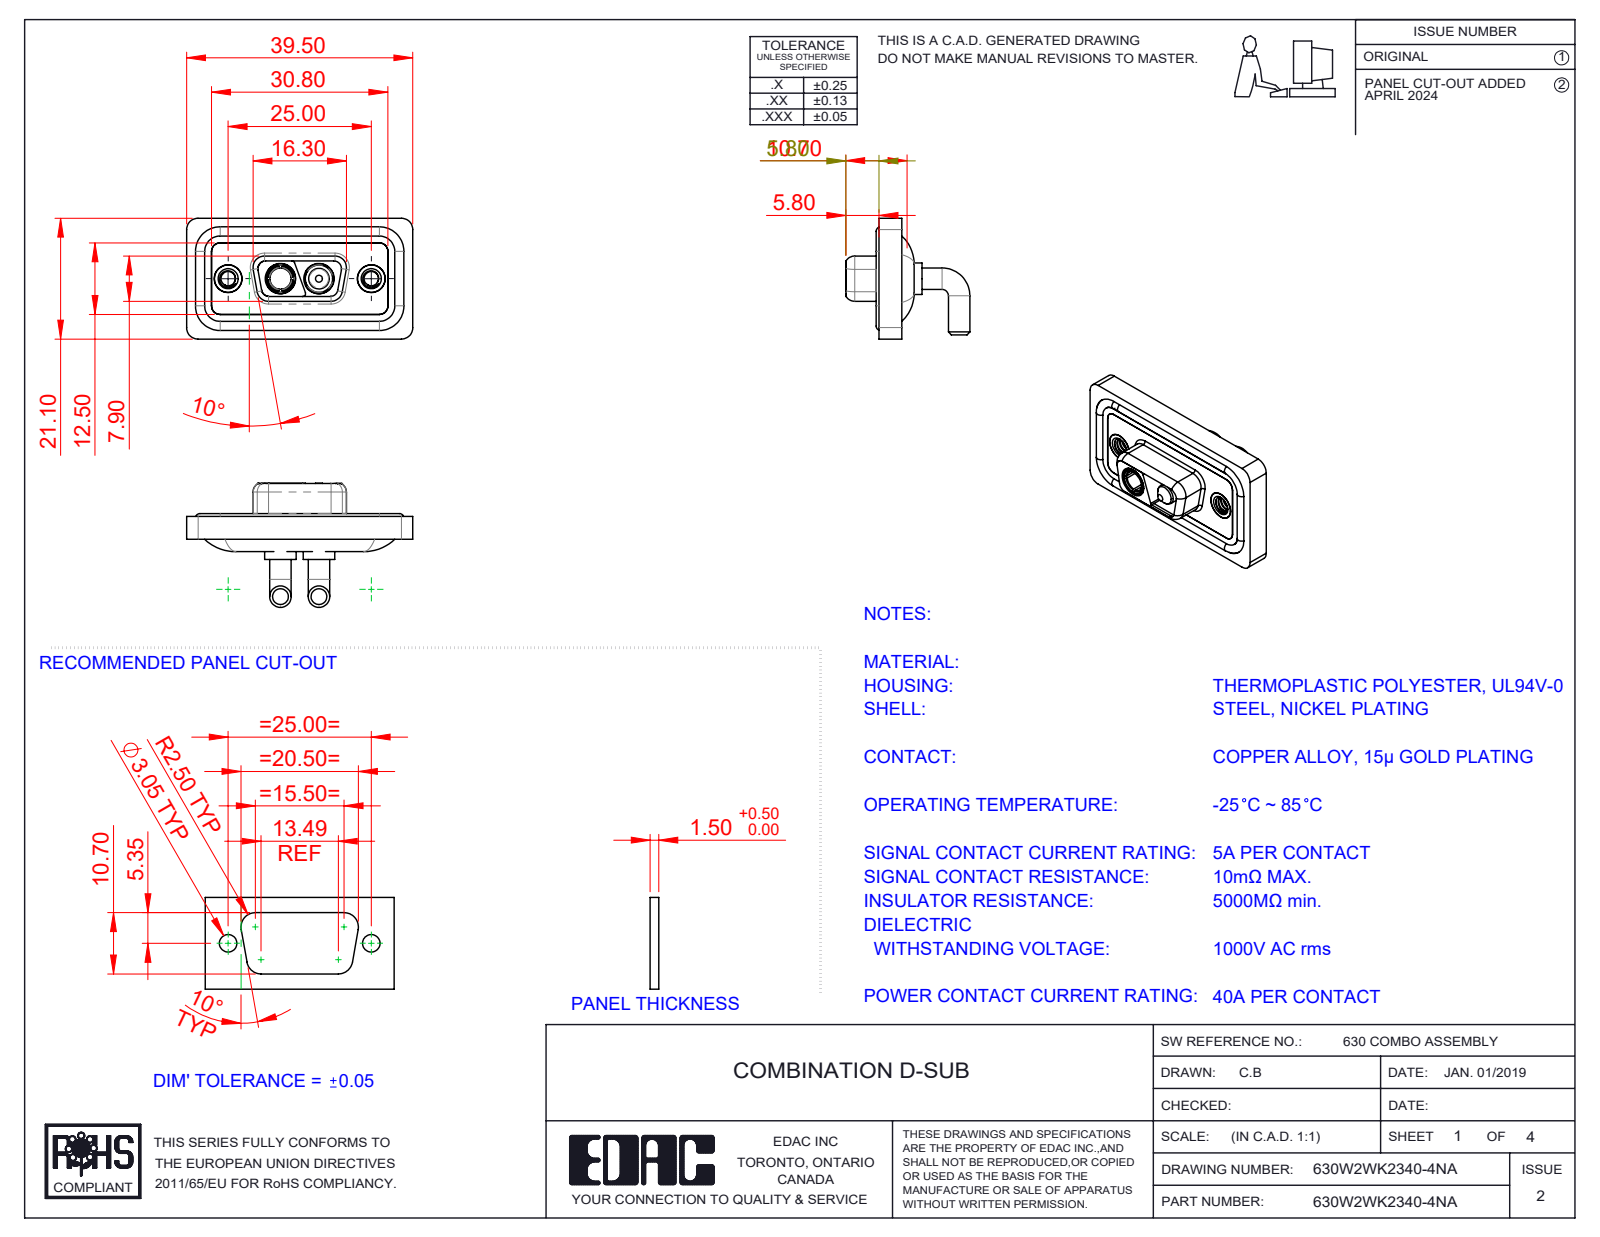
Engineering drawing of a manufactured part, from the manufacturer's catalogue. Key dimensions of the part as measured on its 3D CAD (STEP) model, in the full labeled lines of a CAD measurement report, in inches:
Part name (STEP PRODUCT): Power Socket_40A RA; 630W2WK2340-4NA; 630Combo Shell Front_09 Contacts; 630Combo Shell Rear_09 Contacts (+4 more)
STEP written by: SolidWorks 2023 (CONFIG_CONTROL_DESIGN)
Units: inches
Bodies: 11 solids, 502 faces (144 planar, 233 cylindrical, 125 other)
Overall size (bounding box): 1.555 × 0.854 × 0.831
Volume: 0.296 in³ · Surface area: 11.76 in²
Round holes (diameter × count): ⌀0.191 ×4, ⌀0.098 ×2, ⌀0.157 ×2, ⌀0.159 ×2, ⌀0.197 ×2, ⌀0.209 ×2, ⌀0.146 ×1
Round bosses / shafts (diameter × count): ⌀0.148 ×4, ⌀0.063 ×4, ⌀0.217 ×2, ⌀0.205 ×2, ⌀0.195 ×2, ⌀0.189 ×2, ⌀0.187 ×2, ⌀0.195 ×1
Partial cylindrical surfaces — rounded edges, fillets, slot ends (radius × count): R0.059 ×18, R0.079 ×18, R0.053 ×8, R0.063 ×8, R0.02 ×6, R0.01 ×4, R0.024 ×4, R0.026 ×4
Main face-to-face distances: 0.016, 0.043, 0.114, 0.071, 0.098, 0.063, 0.122, 0.083, 0.146, 0.059
Hole centre spacings: 0.36, 0.624, 0.265, 0.984
